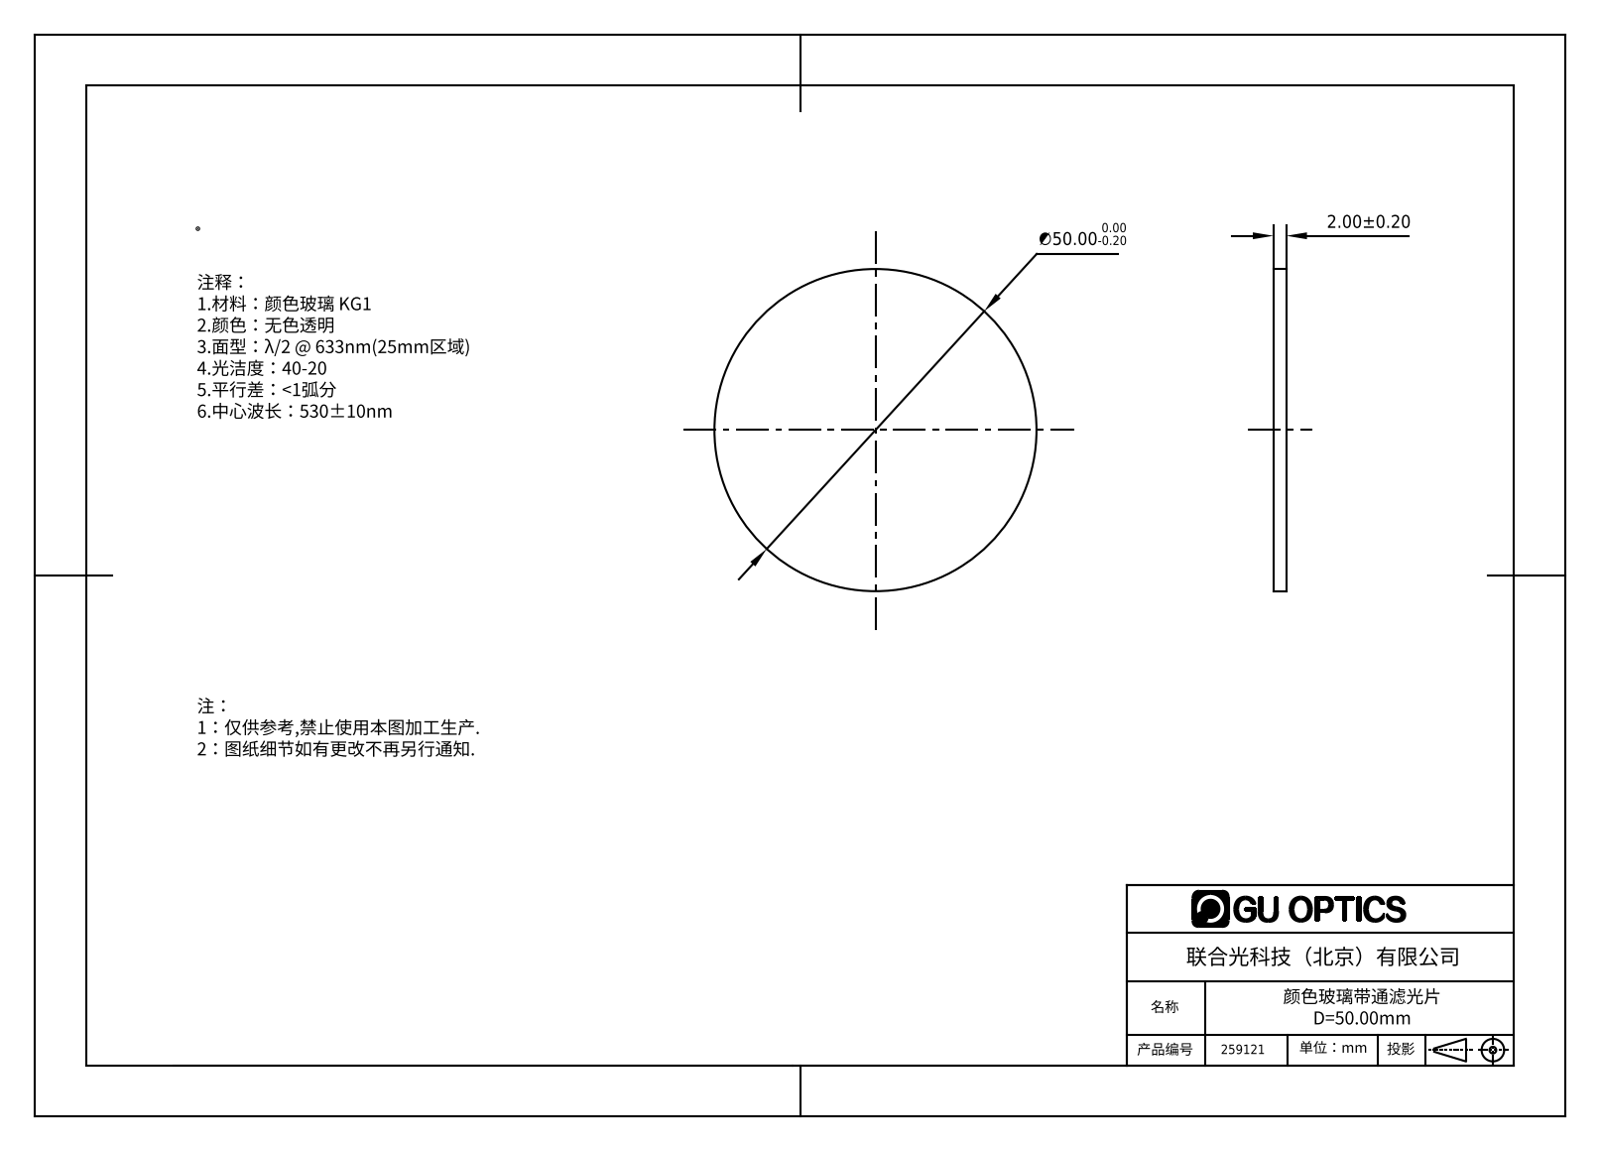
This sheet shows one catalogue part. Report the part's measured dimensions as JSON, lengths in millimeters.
{"part_name": "258514", "step_written_by": "SolidWorks 2016 (AUTOMOTIVE_DESIGN)", "units": "millimeters", "bodies": {"solids": 1, "faces": 4, "planar": 2, "cylindrical": 2, "other": 0}, "overall_size": [50, 50, 2], "volume_mm3": 3927, "surface_area_mm2": 4241, "round_bosses_or_shafts": [[50, 1]], "face_to_face_distances": [2]}
